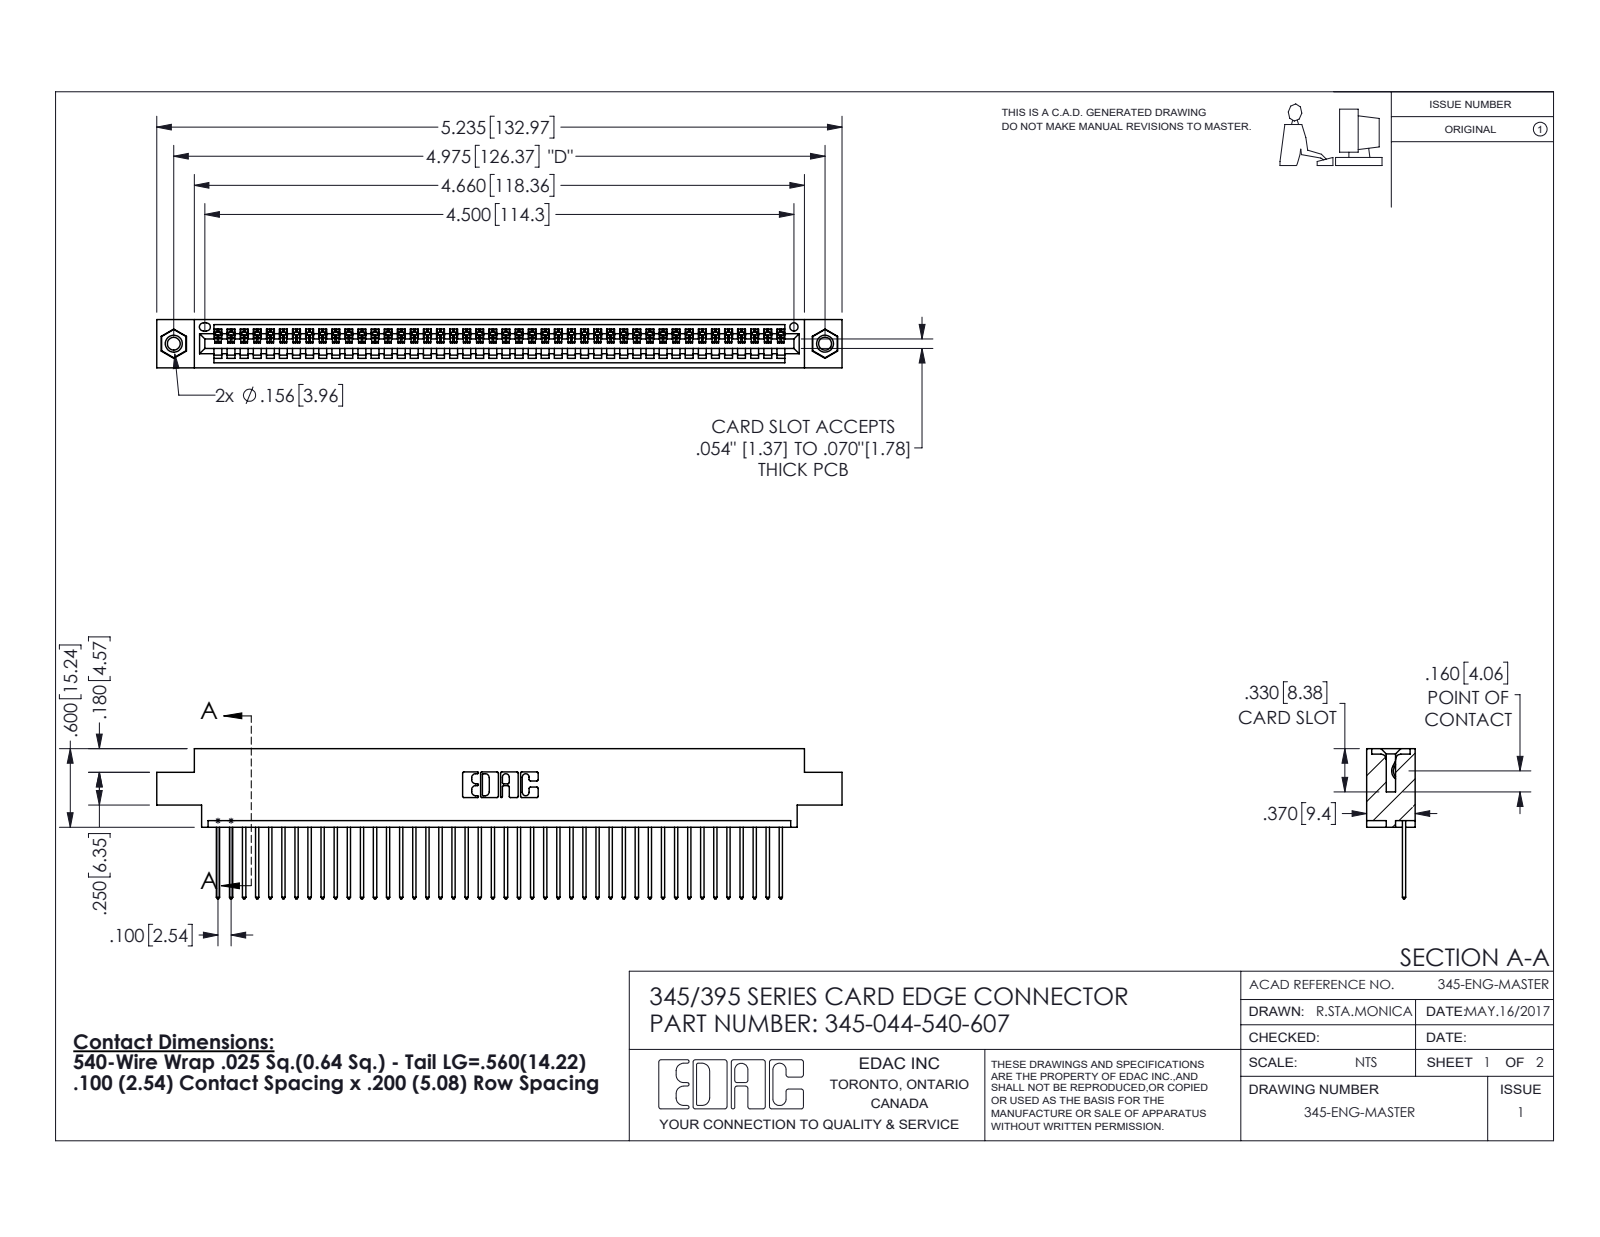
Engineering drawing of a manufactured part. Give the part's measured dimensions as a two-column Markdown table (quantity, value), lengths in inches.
| quantity | value |
| --- | --- |
| part name | 345-292-001_345-293-140; 345-044-540-607; 345-250-001_345-250-005-103; 345 Part_0.170 Offset - 0.156 Dia-TI |
| STEP written by | SolidWorks 2016 (CONFIG_CONTROL_DESIGN) |
| units | inches |
| bodies | 47 solids, 2742 faces (1876 planar, 850 cylindrical, 16 other) |
| overall size | 5.235 × 1.147 × 0.37 |
| volume | 0.768 in³ |
| surface area | 26.86 in² |
| round holes (diameter × count) | 0.098 × 2, 0.125 × 2, 0.156 × 2, 0.064 × 1 |
| round bosses / shafts (diameter × count) | 0.155 × 2 |
| partial cylindrical surfaces (radius × count) | 0.006 × 88, 0.01 × 88, 0.01 × 22, 0.007 × 6, 0.031 × 6, 0.026 × 3, 0.031 × 2, 0.04 × 2 |
| main face-to-face distances | 0.072, 0.298, 0.37, 0.098, 0.272, 0.025, 0.2, 0.225, 0.175, 0.149 |
| hole center spacings | 0.27, 4.739, 4.975 |
